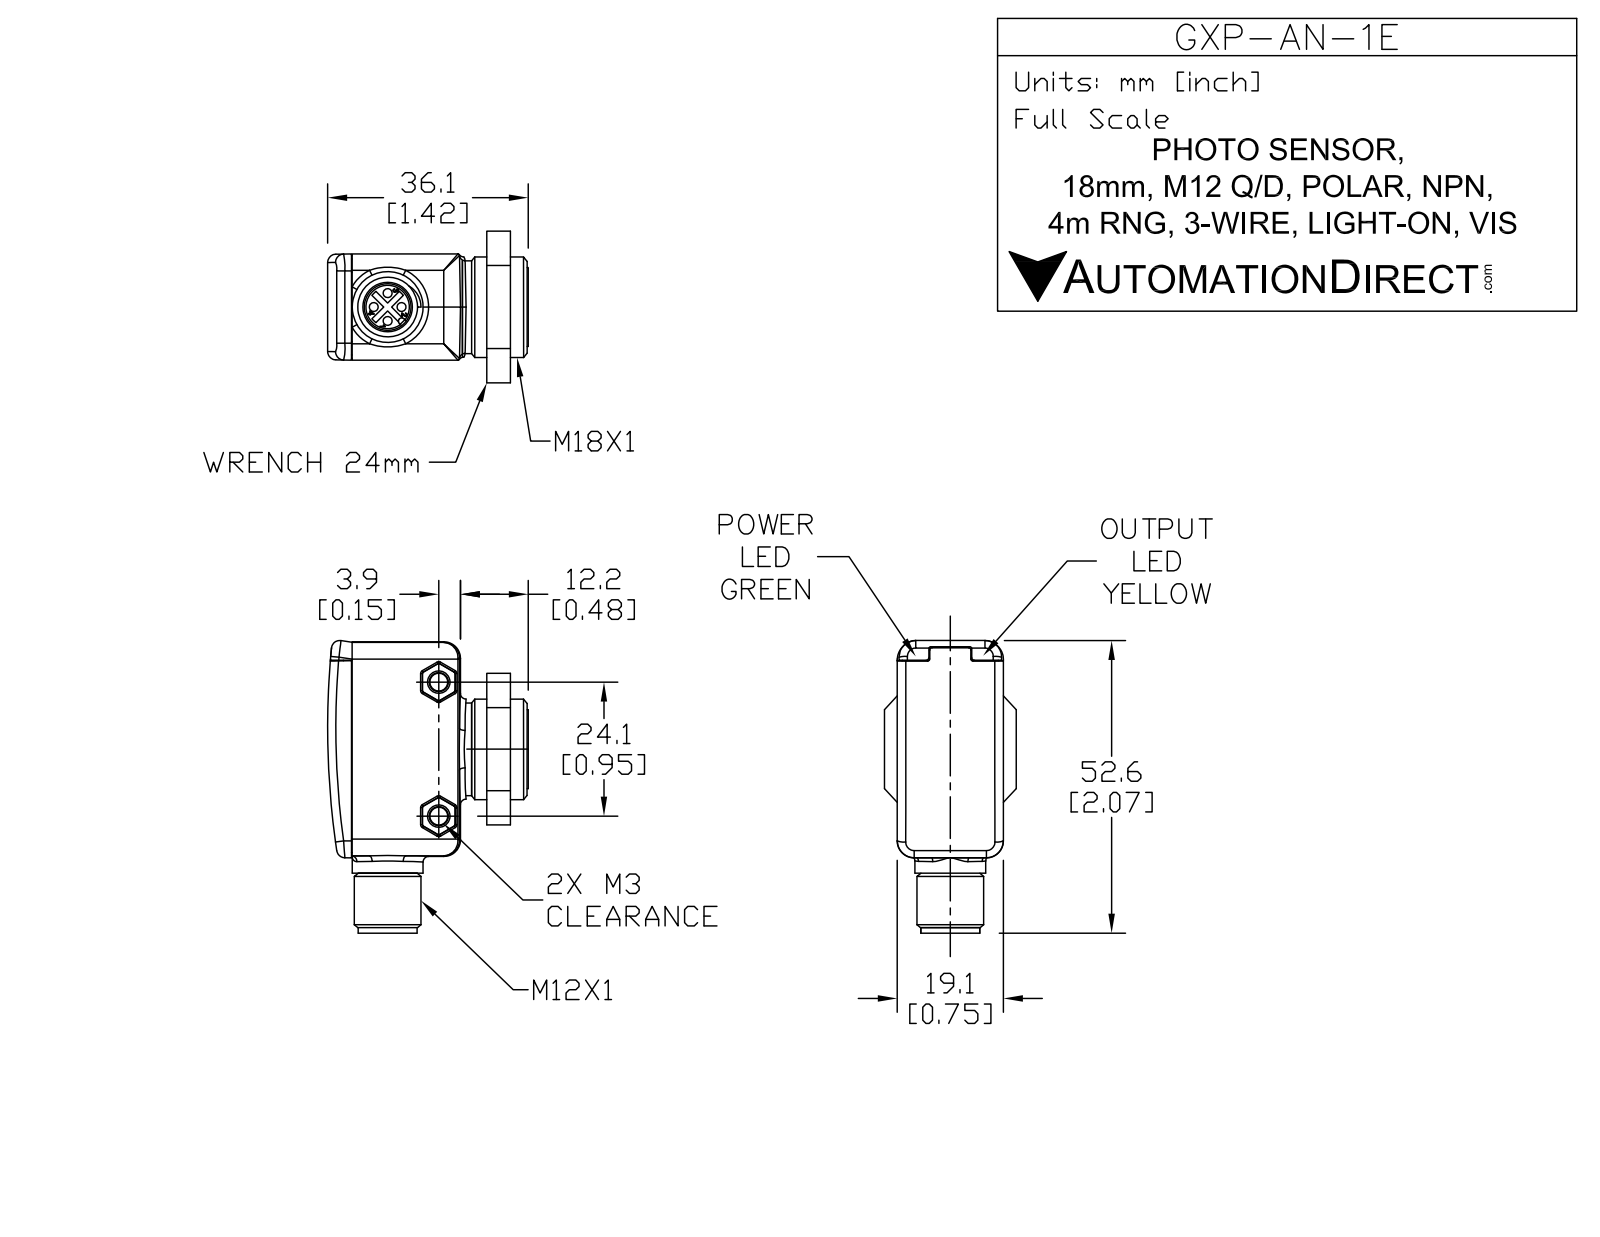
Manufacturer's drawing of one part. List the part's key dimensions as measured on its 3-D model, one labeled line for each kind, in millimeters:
Part name (STEP PRODUCT): GXP-AN-1E
STEP written by: SolidWorks 2013 (AUTOMOTIVE_DESIGN)
Units: millimetres
Bodies: 1 solid, 107 faces (60 planar, 33 cylindrical, 14 other)
Overall size (bounding box): 52.66 × 36.1 × 23.85
Volume: 21 253 mm³ · Surface area: 6 452 mm²
Round holes (diameter × count): ⌀3.2 ×2, ⌀8.36 ×1
Round bosses / shafts (diameter × count): ⌀18 ×1, ⌀17.5 ×1, ⌀14.2 ×1, ⌀12.68 ×1, ⌀11.55 ×1, ⌀10.6 ×1
Partial cylindrical surfaces — rounded edges, fillets, slot ends (radius × count): R1.5 ×8, R1 ×4, R139.57 ×1
Main face-to-face distances: 19.1, 7.2, 2.12, 9.32, 19.2, 5, 2.88, 12.2, 38.8, 5.95
Hole centre spacings: 24.1
